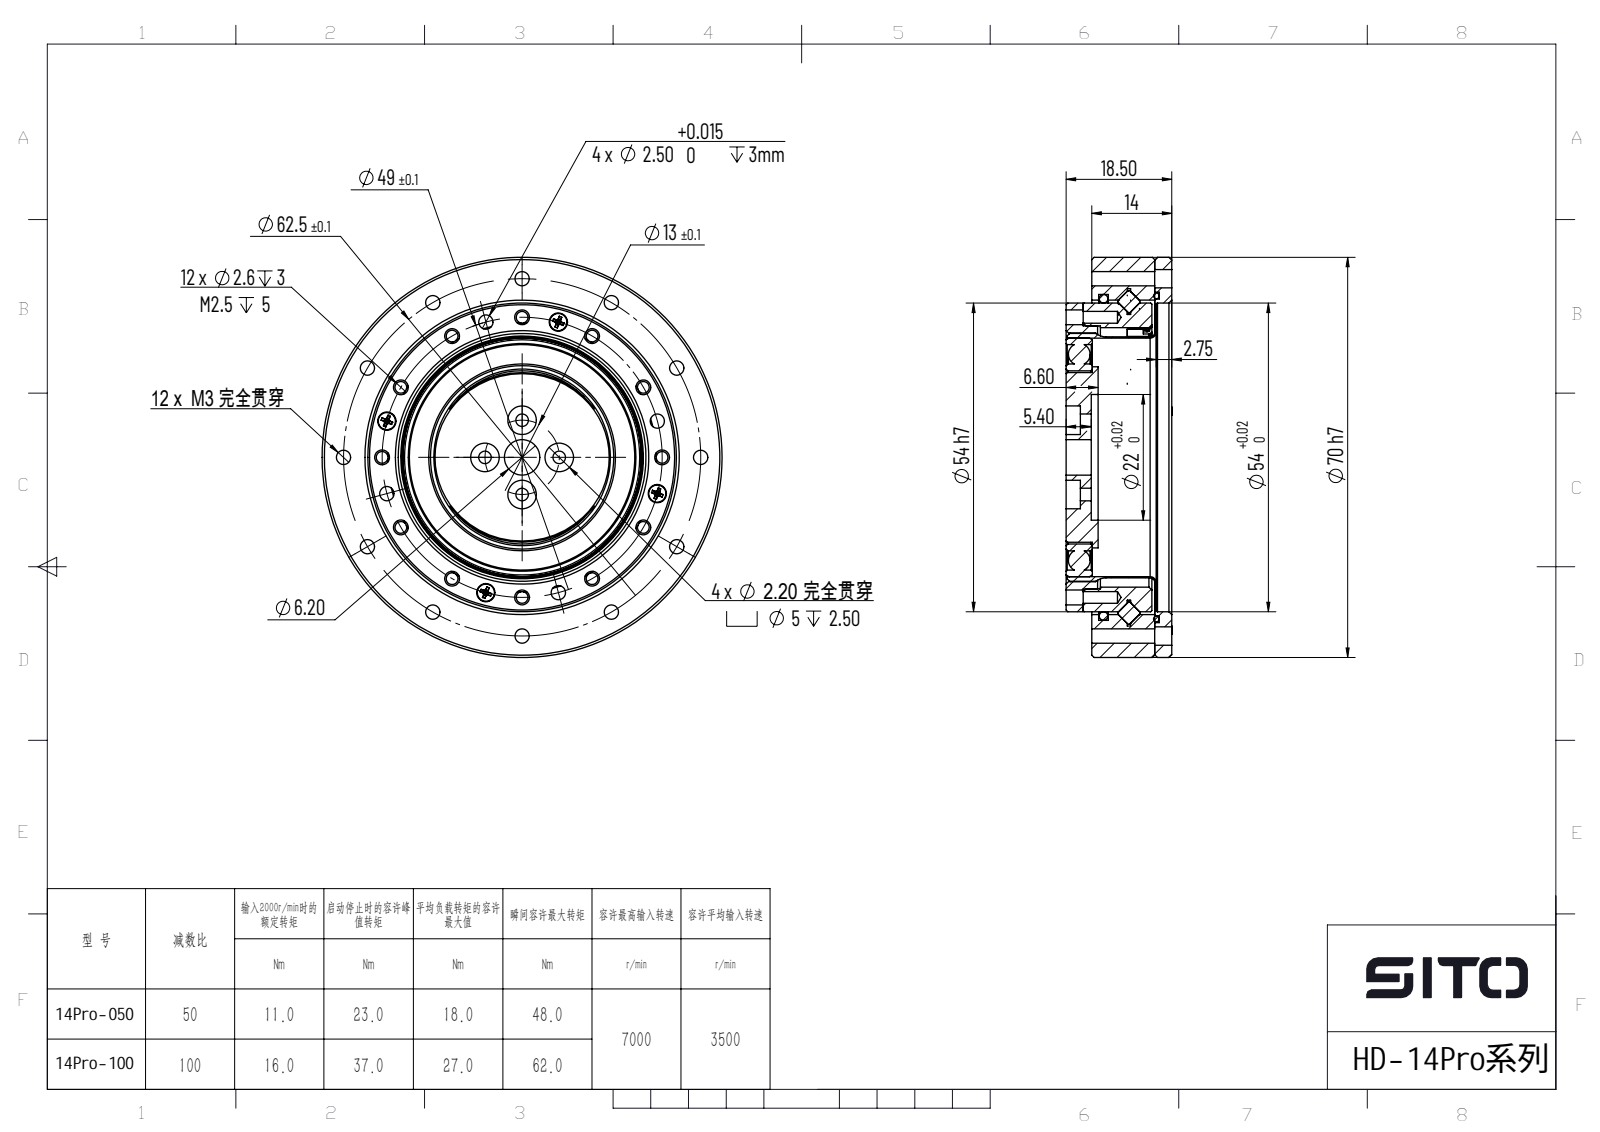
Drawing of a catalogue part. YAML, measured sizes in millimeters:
part_name: "HD-14Pro-xxx; HD-14Pro_006; HD-14Pro???? <1>; HD-14Pro_005 (+8 more)"
step_written_by: "ONSHAPE BY PTC INC, 1.201 (AP242_MANAGED_MODEL_BASED_3D_ENGINEERING_MIM_LF)"
units: millimeters
bodies: {solids: 70, faces: 650, planar: 260, cylindrical: 175, other: 215}
overall_size: [70, 70, 18.57]
volume: 37793
surface_area: 38479
round_holes:
  - {diameter: 2.5, count: 16}
  - {diameter: 2.6, count: 12}
  - {diameter: 2.05, count: 10}
  - {diameter: 2.2, count: 8}
  - {diameter: 3.2, count: 6}
  - {diameter: 1.6, count: 4}
  - {diameter: 4.2, count: 4}
  - {diameter: 5, count: 4}
  - {diameter: 1.25, count: 1}
  - {diameter: 1.7, count: 1}
  - {diameter: 6.2, count: 1}
  - {diameter: 22, count: 1}
round_bosses_or_shafts:
  - {diameter: 3, count: 56}
  - {diameter: 4, count: 4}
  - {diameter: 2, count: 4}
  - {diameter: 1.73, count: 4}
  - {diameter: 70, count: 1}
  - {diameter: 55.4, count: 1}
  - {diameter: 54, count: 1}
  - {diameter: 49.98, count: 1}
partial_cylinders:
  - {radius: 1.02, count: 2}
  - {radius: 1.03, count: 2}
  - {radius: 2, count: 1}
face_to_face_distances: [3, 15.5, 11, 14, 4.5, 18.5, 1.5, 12.5, 8.9, 2.86]
hole_center_spacings: [24.5, 34.65, 15.83, 39.71, 42.44, 47.33, 22.23, 34.36]
